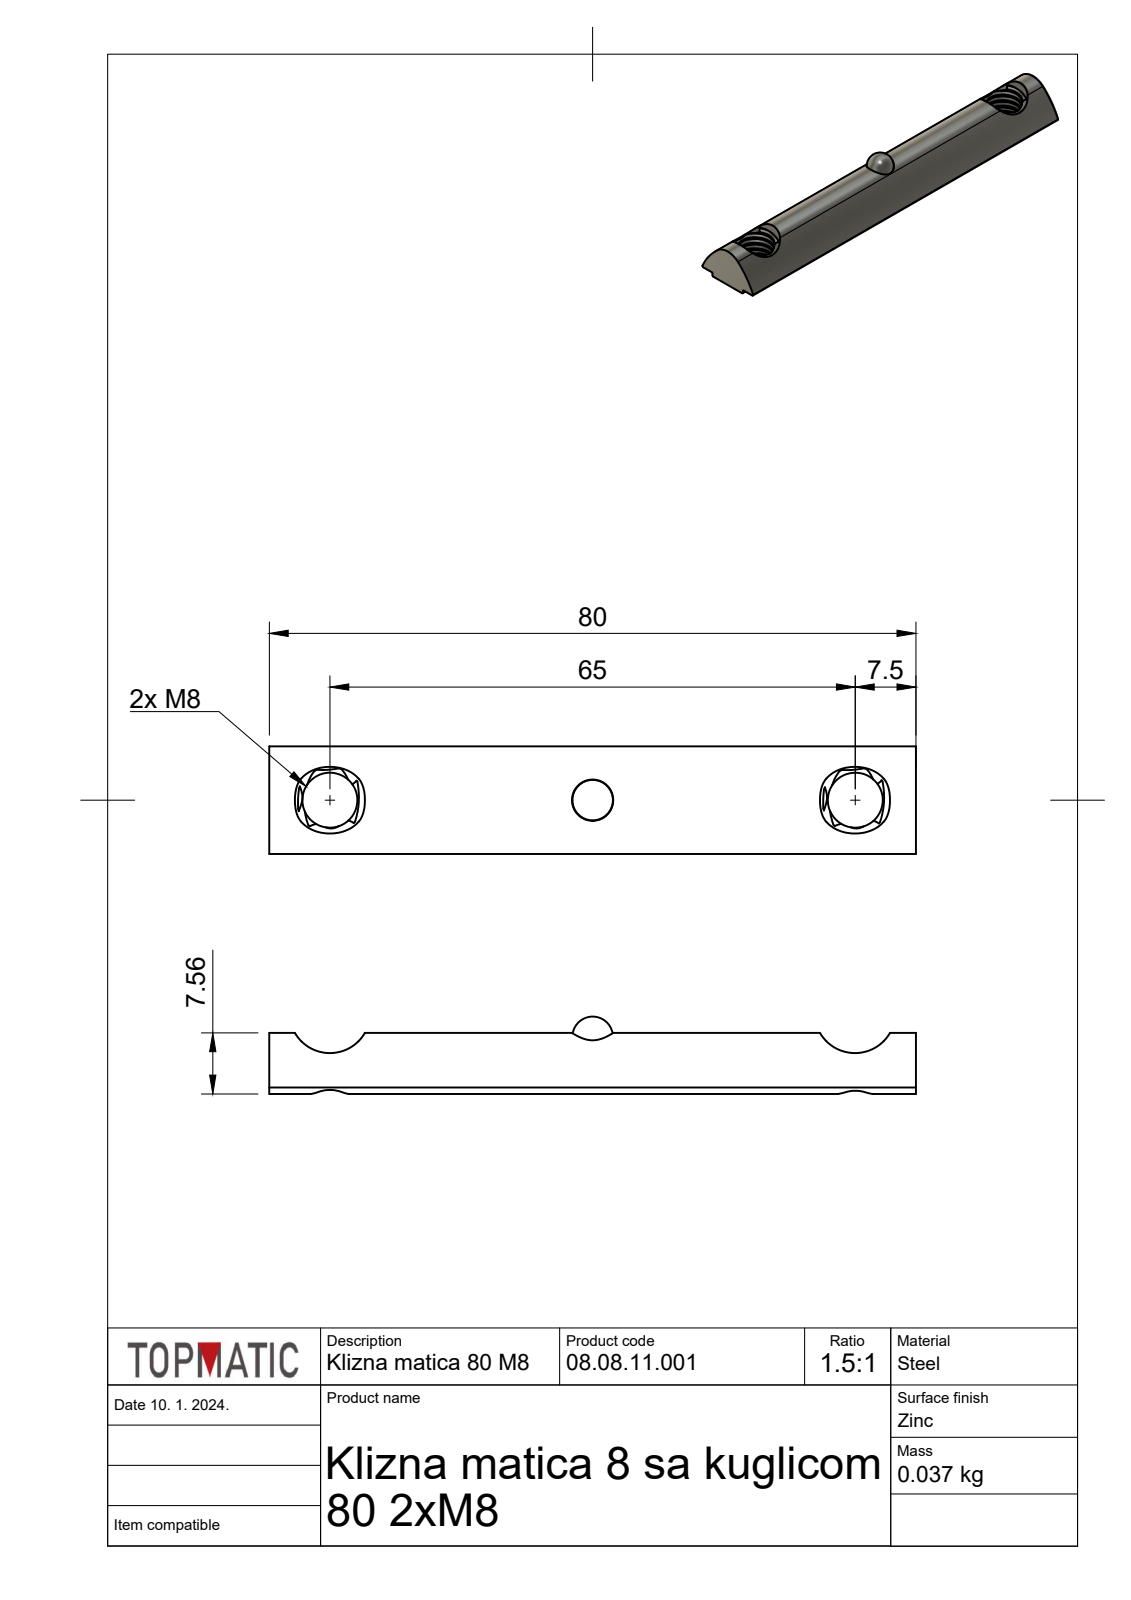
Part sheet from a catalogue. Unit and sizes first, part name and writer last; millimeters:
Units: millimetres
Overall size (bounding box): 80 × 13.3 × 9.56
Round holes (diameter × count): ⌀6.8 ×2, ⌀8.17 ×2, ⌀5.1 ×1
Partial cylindrical surfaces — rounded edges, fillets, slot ends (radius × count): R0.2 ×6, R5 ×2, R16 ×2, R4 ×1
Main face-to-face distances: 0.8, 80, 8
Hole centre spacings: 32.5, 65
Volume: 4 744 mm³ · Surface area: 3 269 mm²
Bodies: 2 solids, 76 faces (9 planar, 47 cylindrical, 20 other)
Part name (STEP PRODUCT): klizna_matica_8x80.prt.f3d
STEP written by: Autodesk Translation Framework v12.14.0.127 (AUTOMOTIVE_DESIGN)
